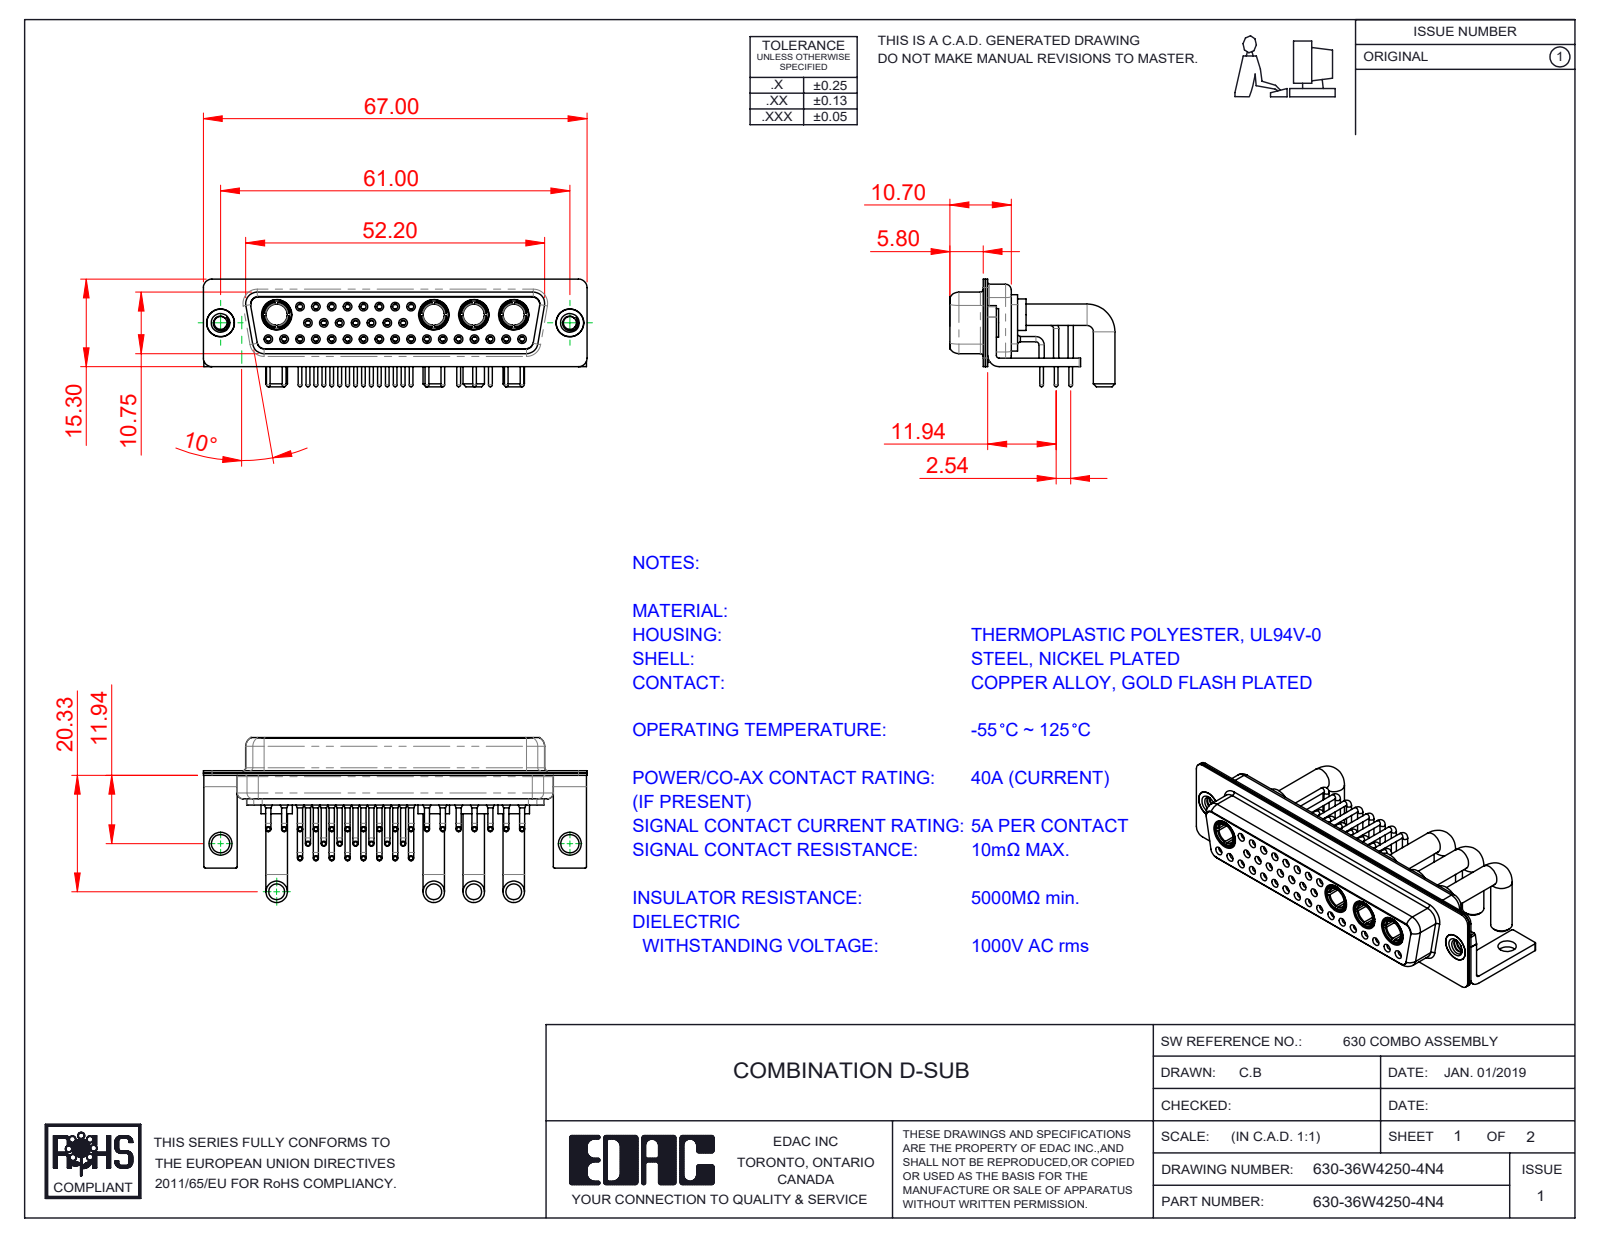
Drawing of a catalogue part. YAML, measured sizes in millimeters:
part_name: "630Combo Shell Front_50 Contacts; 630Combo Housing_36W4; 630Combo Contact Row 3; 630Combo Threaded Rivet_3 (+6 more)"
step_written_by: "SolidWorks 2020 (CONFIG_CONTROL_DESIGN)"
units: millimeters
bodies: {solids: 47, faces: 2327, planar: 683, cylindrical: 991, other: 653}
overall_size: [67, 28.8, 18.8]
volume: 8234
surface_area: 16868
round_holes:
  - {diameter: 0.9, count: 32}
  - {diameter: 1.1, count: 32}
  - {diameter: 1.5, count: 32}
  - {diameter: 2, count: 32}
  - {diameter: 1.6, count: 24}
  - {diameter: 1.7, count: 8}
  - {diameter: 4.85, count: 6}
  - {diameter: 3.7, count: 4}
  - {diameter: 5.3, count: 4}
  - {diameter: 2.26, count: 2}
  - {diameter: 3.2, count: 2}
  - {diameter: 4, count: 2}
round_bosses_or_shafts:
  - {diameter: 0.9, count: 33}
  - {diameter: 0.65, count: 32}
  - {diameter: 1.6, count: 9}
  - {diameter: 3.75, count: 8}
  - {diameter: 5.5, count: 4}
  - {diameter: 5.2, count: 4}
  - {diameter: 4.96, count: 4}
  - {diameter: 4.75, count: 4}
partial_cylinders:
  - {radius: 0.25, count: 16}
  - {radius: 1.5, count: 16}
  - {radius: 2, count: 13}
  - {radius: 1.35, count: 12}
  - {radius: 1.6, count: 8}
  - {radius: 0.5, count: 5}
  - {radius: 0.6, count: 4}
  - {radius: 0.65, count: 4}
face_to_face_distances: [0.4, 1.5, 0.8, 6, 5.6, 5.2, 5.8, 11.28, 1.82, 10.35]
hole_center_spacings: [2.77, 5.54, 3.16, 8.31, 11.08, 13.85, 16.62, 19.39]
